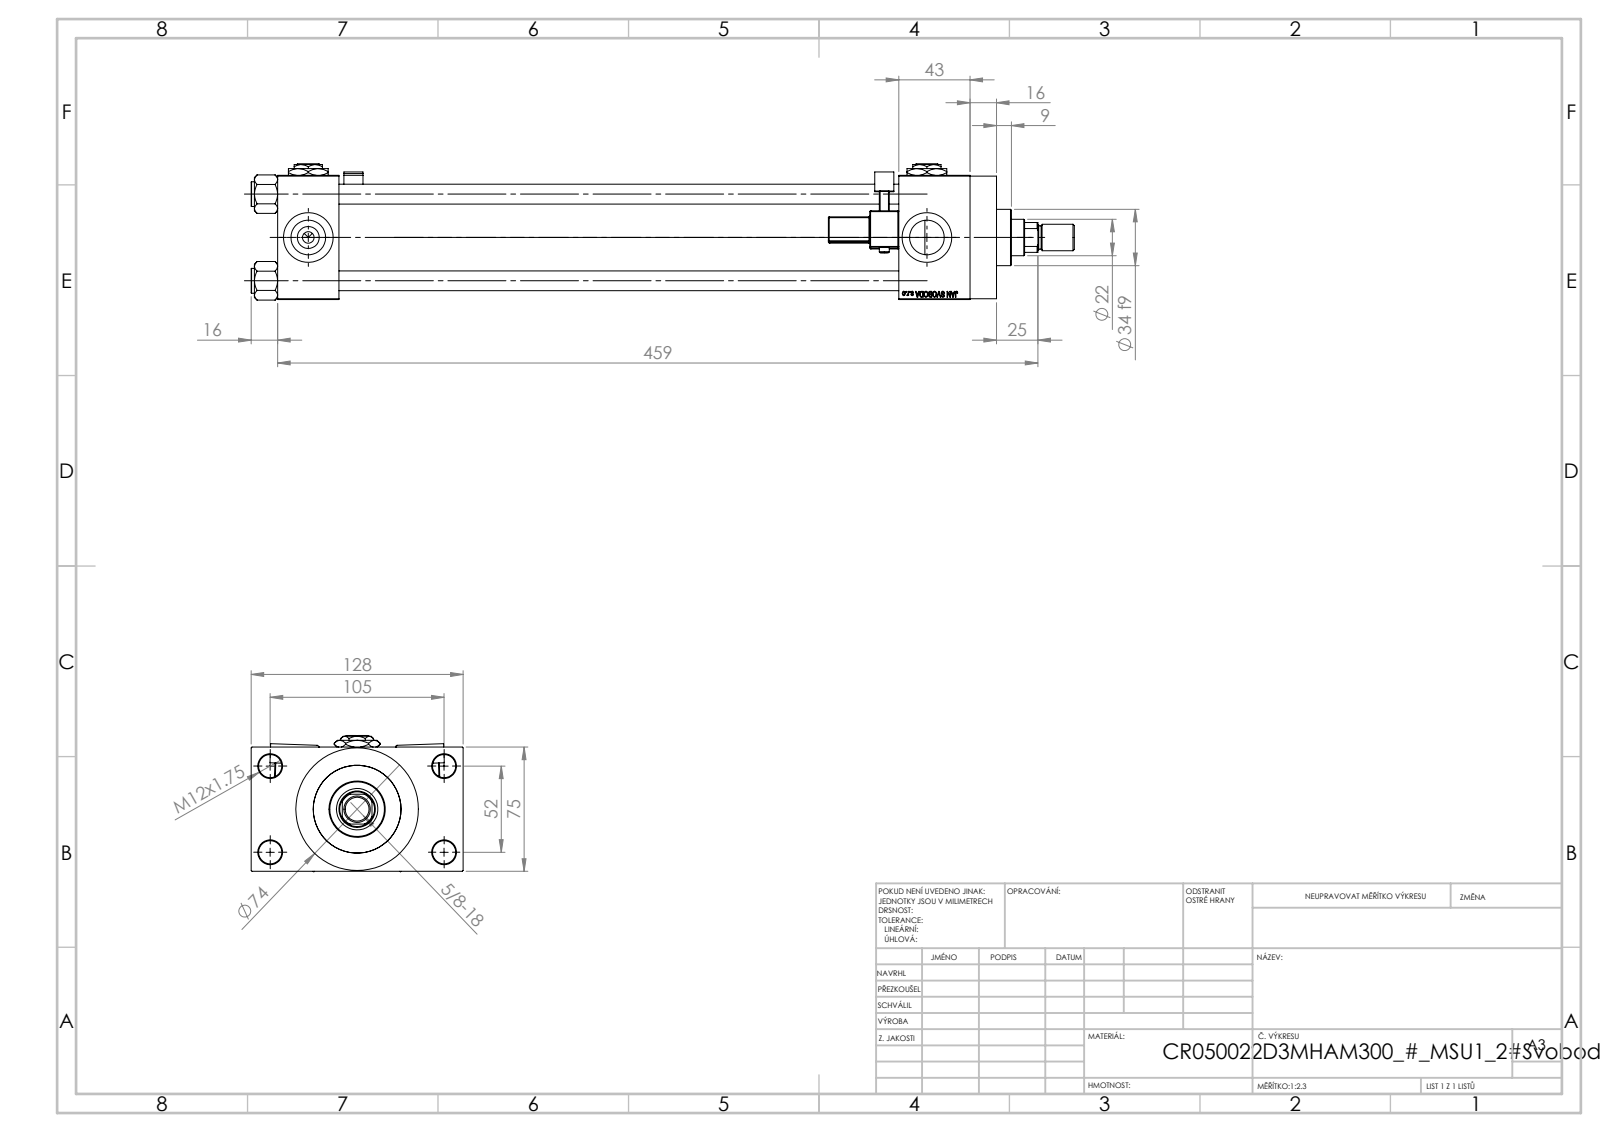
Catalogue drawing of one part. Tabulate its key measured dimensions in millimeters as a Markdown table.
| quantity | value |
| --- | --- |
| part name | V215CR_MSU; Zatka_pro_OIL_PORT; V215CR_VCP_D; V215CR_D_Body (+4 more) |
| STEP written by | SolidWorks 2019 (CONFIG_CONTROL_DESIGN) |
| units | millimeters |
| bodies | 16 solids, 1372 faces (607 planar, 163 cylindrical, 602 other) |
| overall size | 497 × 128 × 82.27 |
| volume | 1 212 000 mm³ |
| surface area | 339 548 mm² |
| round holes (diameter × count) | 12 × 4, 14 × 4, 20.96 × 4, 30 × 4, 7 × 3, 10.5 × 1, 22 × 1, 25 × 1, 41 × 1, 50 × 1, 53 × 1 |
| round bosses / shafts (diameter × count) | 15 × 4, 6 × 2, 74 × 1, 56 × 1, 34 × 1, 16 × 1, 14 × 1 |
| partial cylindrical surfaces (radius × count) | 0.5 × 48, 1 × 2, 2.5 × 2, 4 × 2, 10.5 × 1 |
| main face-to-face distances | 75, 338, 37, 375, 26.5, 101.5, 418, 381, 43, 16 |
| hole center spacings | 26.35, 36.98, 52.3, 58.43, 58.59, 78.65, 94.37, 52 |
